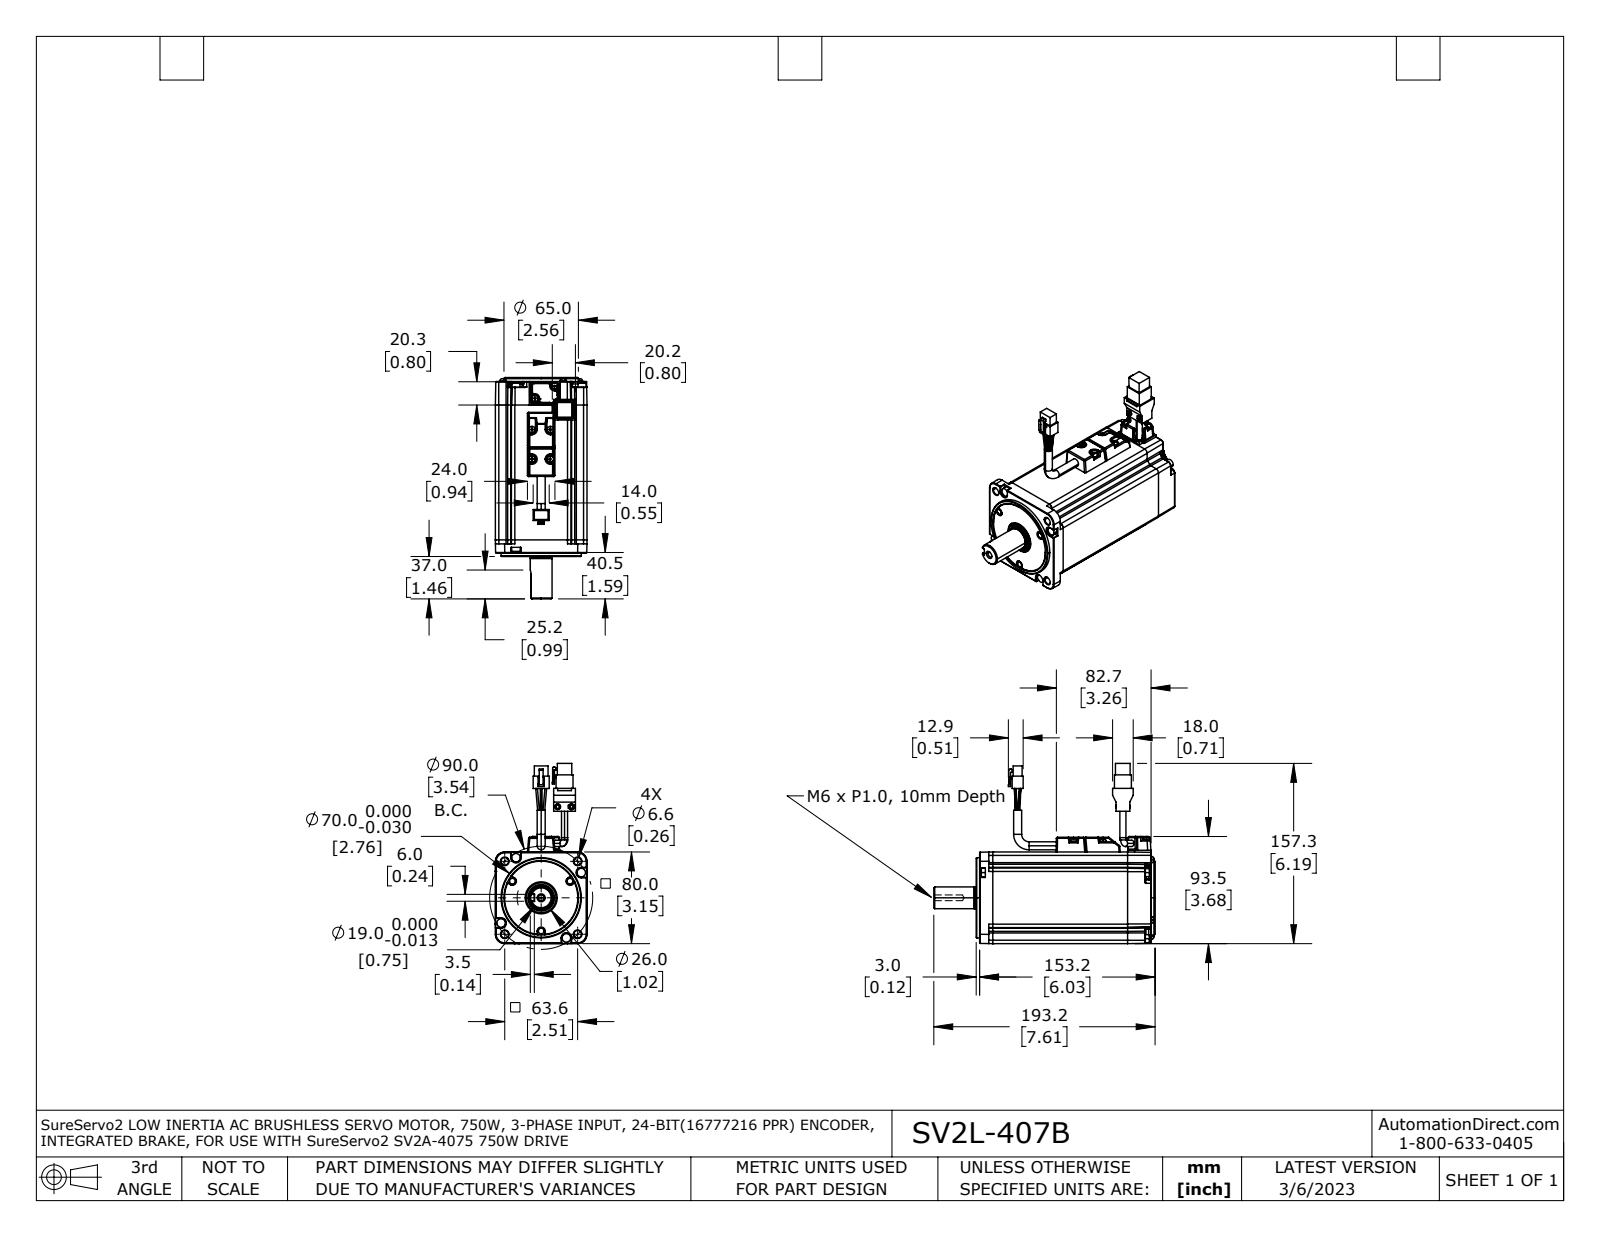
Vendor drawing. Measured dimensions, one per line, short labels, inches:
name: SV2L-407B sr1
written by: SolidWorks 2021 (AUTOMOTIVE_DESIGN)
unit: in
bodies: 1 solid, 974 faces (359 planar, 329 cylindrical, 286 other)
size: 7.606 × 6.193 × 3.15
volume: 55.6 in³; area: 115.6 in²
holes: 4× ⌀0.26, 2× ⌀0.201, 1× ⌀0.11, 1× ⌀0.197, 1× ⌀1.024, 1× ⌀1.102, 1× ⌀2.559
bosses: 12× ⌀0.217, 6× ⌀0.276, 6× ⌀0.059, 4× ⌀0.295, 3× ⌀0.197, 2× ⌀0.181, 2× ⌀0.142, 2× ⌀0.098
rounds: 52× R0.039, 28× R0.118, 20× R0.008, 20× R0.079, 14× R0.02, 12× R0.012, 8× R0.072, 8× R0.073
face distances: 3.15, 0.551, 2.598, 2.047, 6.13, 3.228, 0.138, 0.098, 6.031, 5.894
hole spacings: 1.772, 2.506, 3.543, 0.472, 1.889, 1.999, 2.614, 2.962
